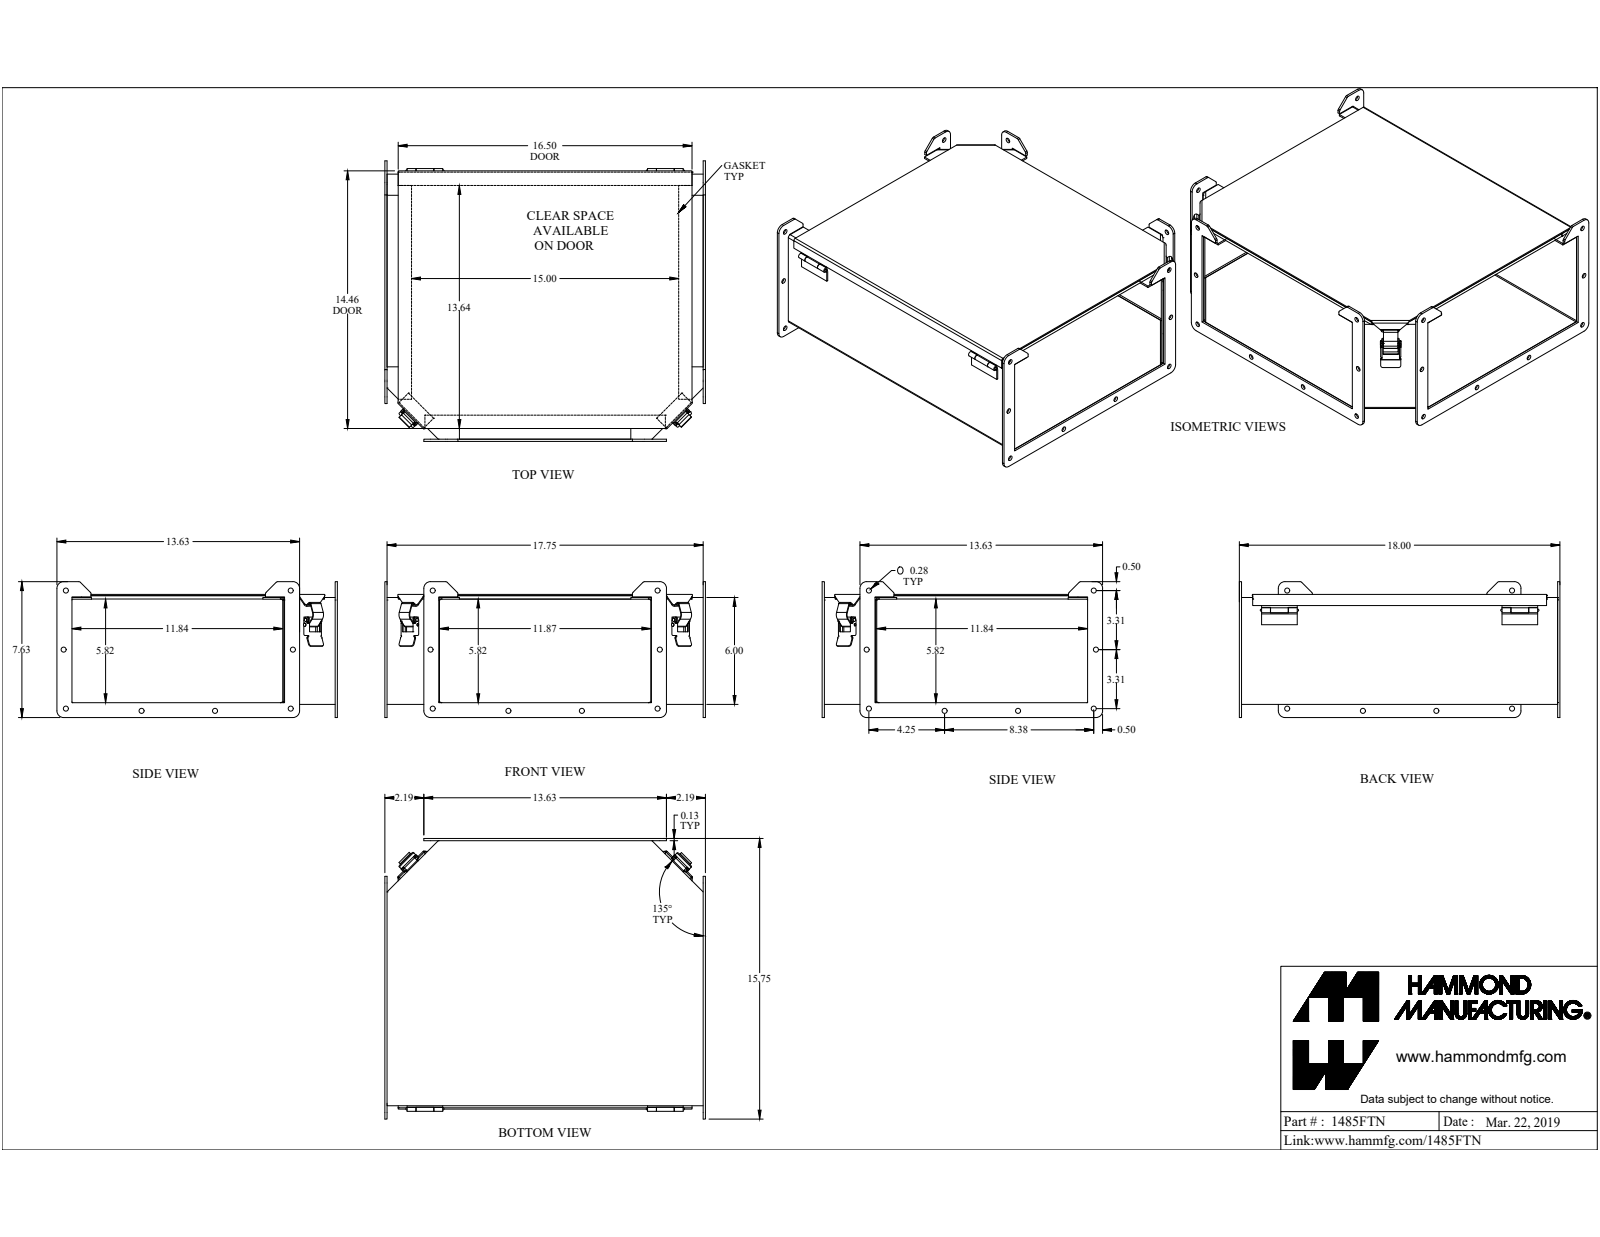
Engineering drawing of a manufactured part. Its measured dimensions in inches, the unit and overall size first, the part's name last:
Units: inches
Overall size (bounding box): 18 × 15.748 × 7.625
Round holes (diameter × count): ⌀0.281 ×16, ⌀0.13 ×4, ⌀0.164 ×4, ⌀0.125 ×1
Round bosses / shafts (diameter × count): ⌀0.187 ×6, ⌀0.156 ×4, ⌀0.125 ×2, ⌀0.275 ×1, ⌀0.125 ×1
Partial cylindrical surfaces — rounded edges, fillets, slot ends (radius × count): R0.125 ×16, R0.016 ×14, R0.035 ×8, R0.039 ×8, R0.375 ×8, R0.048 ×6, R0.076 ×6, R0.143 ×6
Main face-to-face distances: 0.095, 6.005, 6.1, 0.072, 6.077, 6.172, 5.905, 0.125, 17.876, 0.259
Hole centre spacings: 13.173, 0.285, 0.285, 3.315, 3.315, 4.252, 5.564, 6.625
Volume: 77.89 in³ · Surface area: 1 710 in²
Bodies: 23 solids, 538 faces (322 planar, 188 cylindrical, 28 other)
Part name (STEP PRODUCT): 1485FTN
STEP written by: SolidWorks 2019 (CONFIG_CONTROL_DESIGN)
